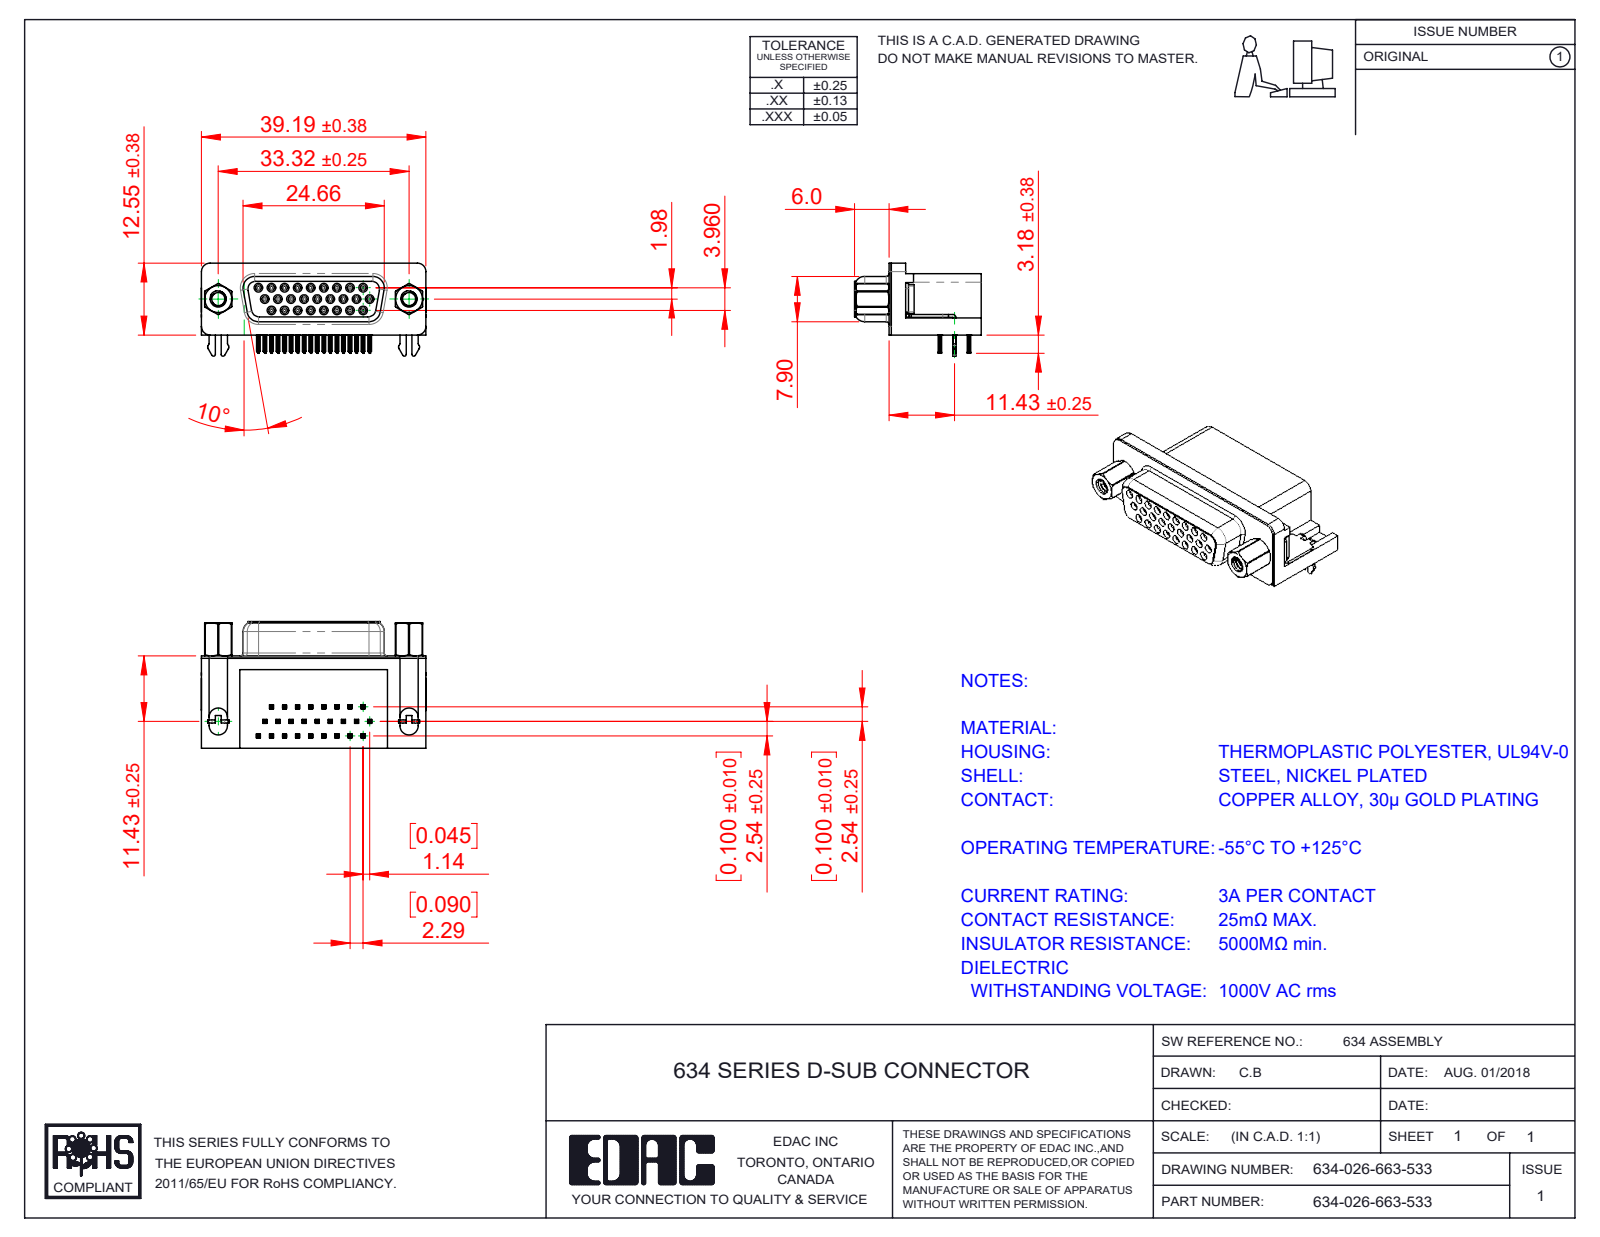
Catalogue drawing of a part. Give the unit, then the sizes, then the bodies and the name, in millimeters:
Units: millimetres
Overall size (bounding box): 39.22 × 22.1 × 16.25
Round holes (diameter × count): ⌀0.8 ×26, ⌀0.9 ×26, ⌀2.26 ×2, ⌀2.29 ×2, ⌀4 ×2, ⌀4.8 ×2, ⌀5 ×2
Round bosses / shafts (diameter × count): ⌀1.2 ×26, ⌀4.9 ×2, ⌀4.75 ×2, ⌀3.9 ×2, ⌀2.79 ×2
Partial cylindrical surfaces — rounded edges, fillets, slot ends (radius × count): R0.1 ×208, R0.15 ×104, R0.35 ×52, R0.34 ×26, R1 ×19, R0.5 ×10, R0.25 ×8, R0.28 ×8
Main face-to-face distances: 0.4, 10.34, 0.35, 15.7, 16.1, 6.65, 2.5, 0.85, 2.9, 10.69
Hole centre spacings: 2.29, 4.57, 2.28, 3.96, 6.05, 2.3, 2.27, 4.58
Volume: 6 567 mm³ · Surface area: 9 537 mm²
Bodies: 34 solids, 4141 faces (1825 planar, 1010 cylindrical, 1306 other)
Part name (STEP PRODUCT): Contact Top; 4-40 Hex Standoff; 634 Shell_26 Socket; 634 Housing_26 Socket (+5 more)
STEP written by: SolidWorks 2016 (CONFIG_CONTROL_DESIGN)
